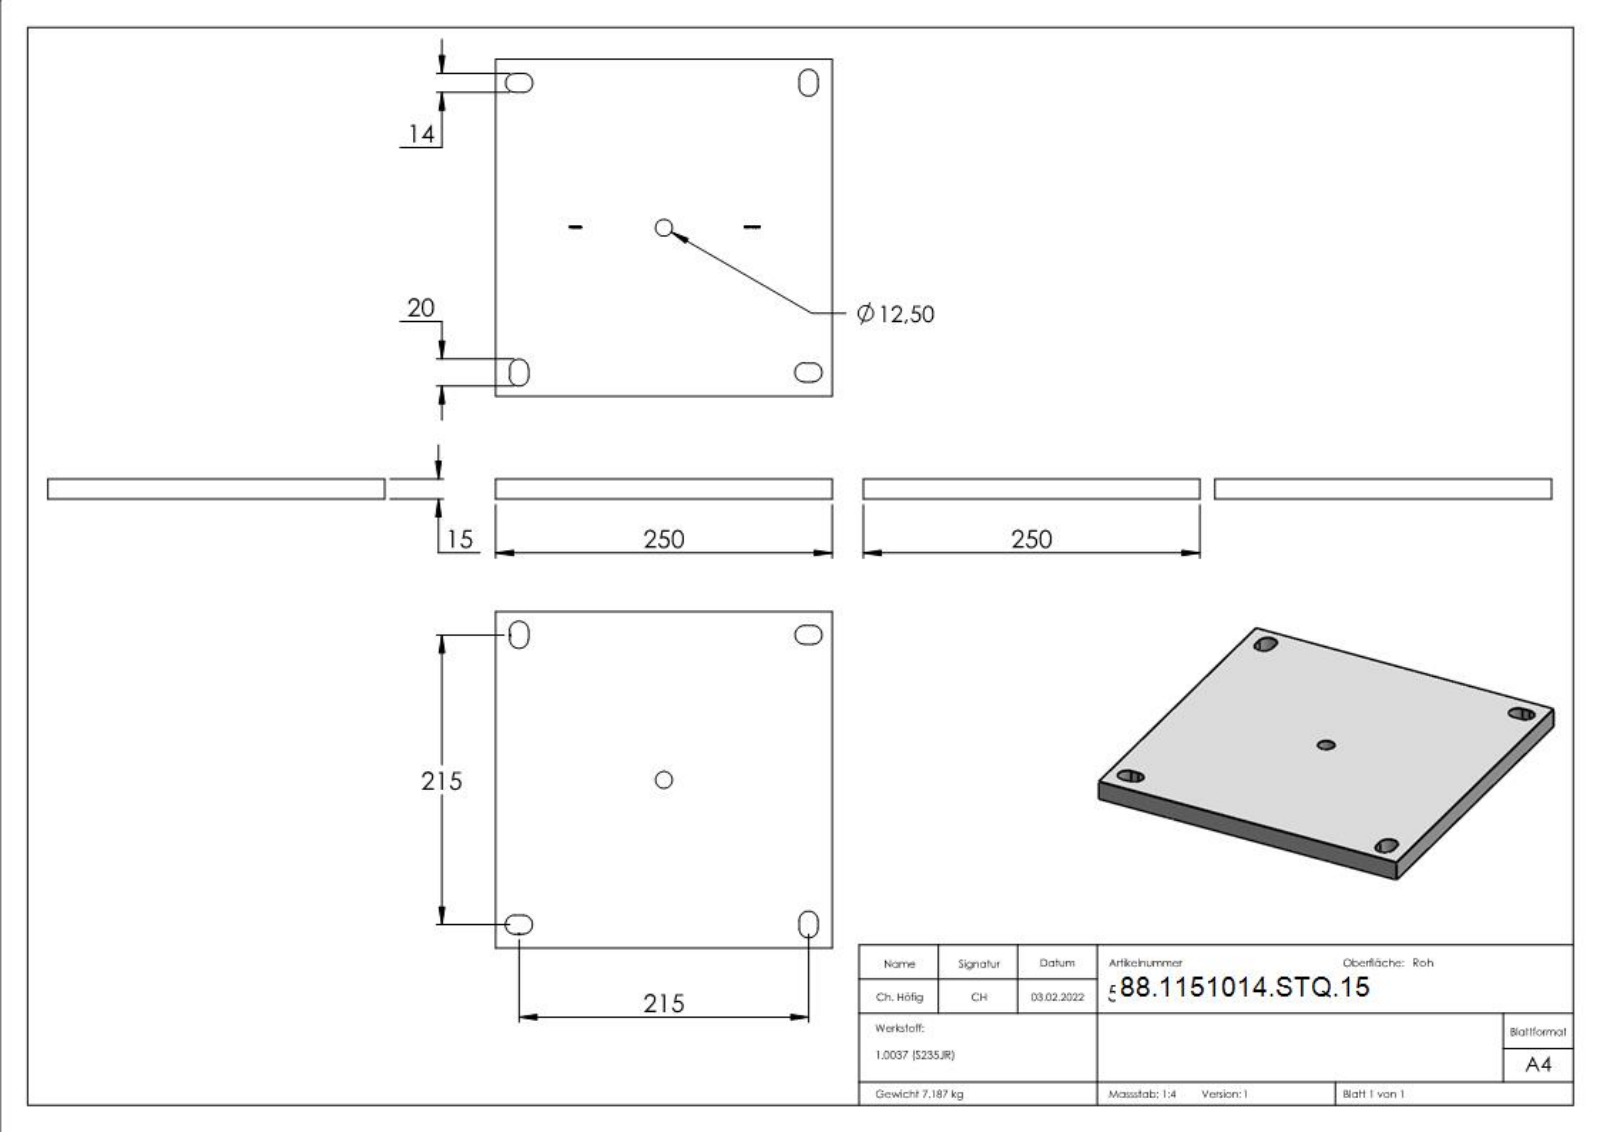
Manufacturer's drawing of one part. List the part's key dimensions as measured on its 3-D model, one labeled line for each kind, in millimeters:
Part name (STEP PRODUCT): 51014-STQ-15
STEP written by: SolidWorks 2018 (CONFIG_CONTROL_DESIGN)
Units: millimetres
Bodies: 1 solid, 271 faces (161 planar, 12 cylindrical, 98 other)
Overall size (bounding box): 250 × 250 × 15
Volume: 921 382 mm³ · Surface area: 141 809 mm²
Round holes (diameter × count): ⌀12.5 ×1
Partial cylindrical surfaces — rounded edges, fillets, slot ends (radius × count): R7 ×8
Main face-to-face distances: 15, 250, 10.5, 24.5, 225.5, 239.5, 14, 215, 229, 201
